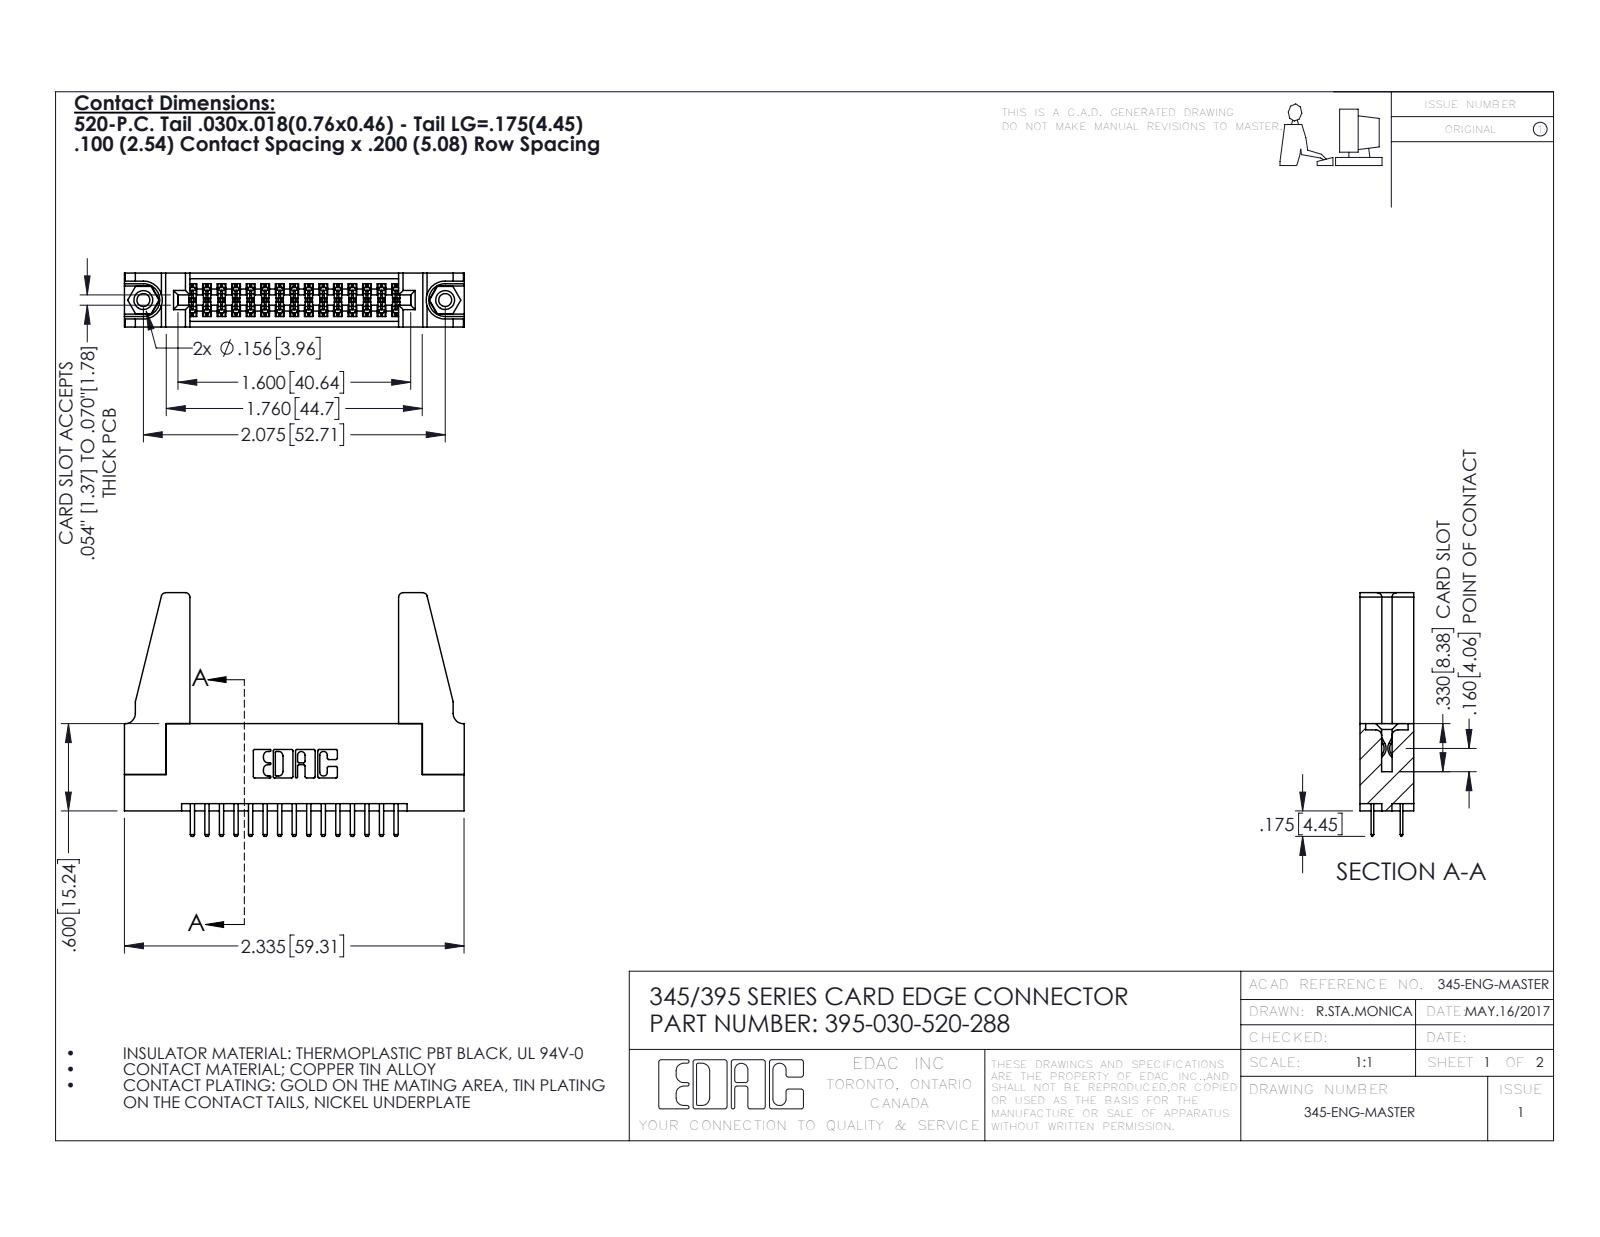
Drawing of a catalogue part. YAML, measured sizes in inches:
part_name: "345-220-078_345-220-088; 345-292-001_345-293-120; 345 Part_Flush Mounting Lugs - 0.156 Dia-TH; 345-250-001_345-250-001-102 (+1 more)"
step_written_by: "SolidWorks 2016 (CONFIG_CONTROL_DESIGN)"
units: inches
bodies: {solids: 35, faces: 1870, planar: 1202, cylindrical: 652, other: 16}
overall_size: [2.336, 1.675, 0.37]
volume: 0.534
surface_area: 16.59
round_holes:
  - {diameter: 0.089, count: 2}
  - {diameter: 0.125, count: 2}
  - {diameter: 0.156, count: 2}
  - {diameter: 0.064, count: 1}
round_bosses_or_shafts:
  - {diameter: 0.155, count: 2}
partial_cylinders:
  - {radius: 0.006, count: 45}
  - {radius: 0.01, count: 34}
  - {radius: 0.01, count: 22}
  - {radius: 0.03, count: 8}
  - {radius: 0.007, count: 6}
  - {radius: 0.031, count: 6}
  - {radius: 0.026, count: 3}
  - {radius: 0.014, count: 2}
face_to_face_distances: [0.37, 0.072, 0.2, 0.298, 0.098, 0.272, 0.025, 0.225, 0.022, 0.072]
hole_center_spacings: [0.27, 1.842, 2.075]
